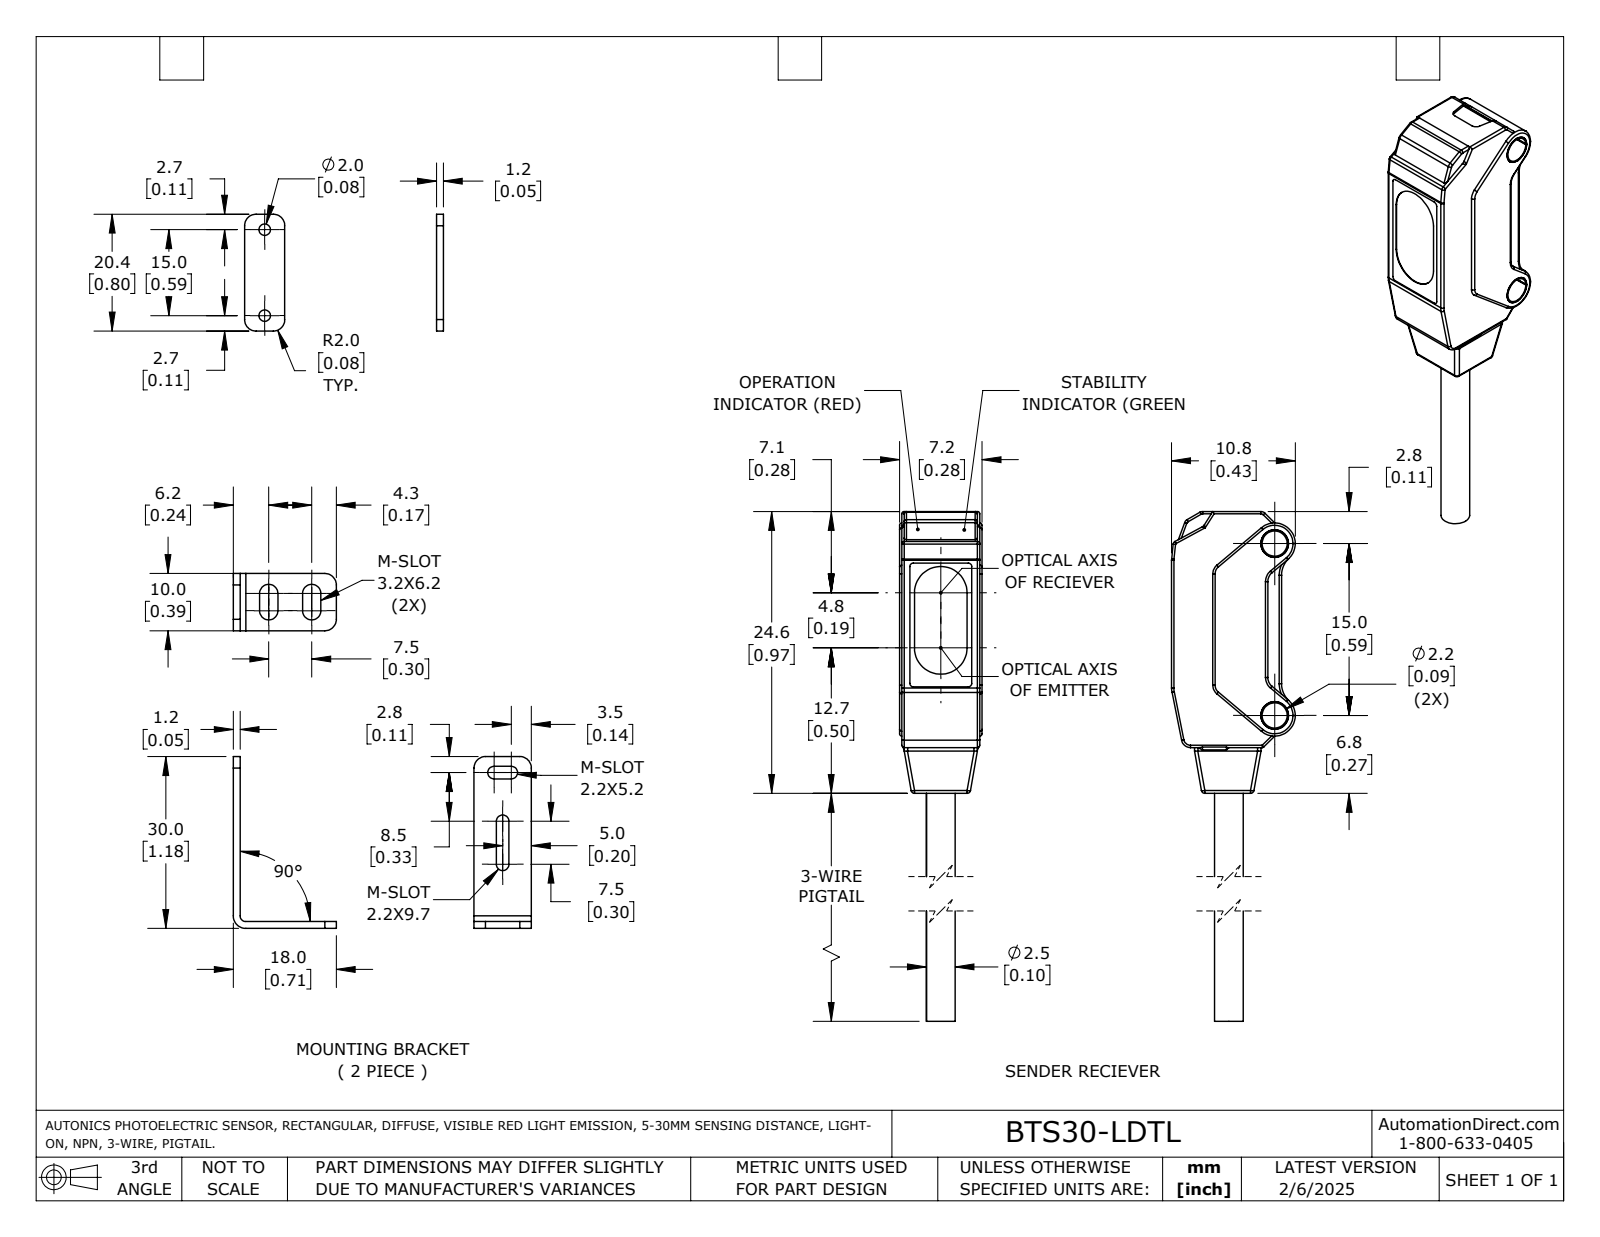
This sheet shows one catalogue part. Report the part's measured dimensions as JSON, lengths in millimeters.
{"part_name": "BTS15-LDTL_BTS15-LDTL-P_BTS15-LDTD_BTS15-LDTD-P_BTS30-LDTL", "step_written_by": "SolidWorks 2024 (AUTOMOTIVE_DESIGN)", "units": "millimeters", "bodies": {"solids": 5, "faces": 622, "planar": 404, "cylindrical": 144, "other": 74}, "overall_size": [41.68, 28.8, 14], "volume_mm3": 2243, "surface_area_mm2": 2664, "round_holes": [[2, 2], [2.2, 2], [2.41, 2]], "round_bosses_or_shafts": [[4, 2], [2.4, 2], [2.5, 1]], "partial_cylinders_radius": [[0.2, 39], [0.3, 14], [2, 11], [0.5, 6], [0.2, 5], [1.1, 4], [1.6, 4], [0.45, 2]], "face_to_face_distances": [1.2, 8.4, 7, 7.2, 8.2, 1.4, 9.6, 6.8, 5.6, 10], "hole_center_spacings": [15]}
